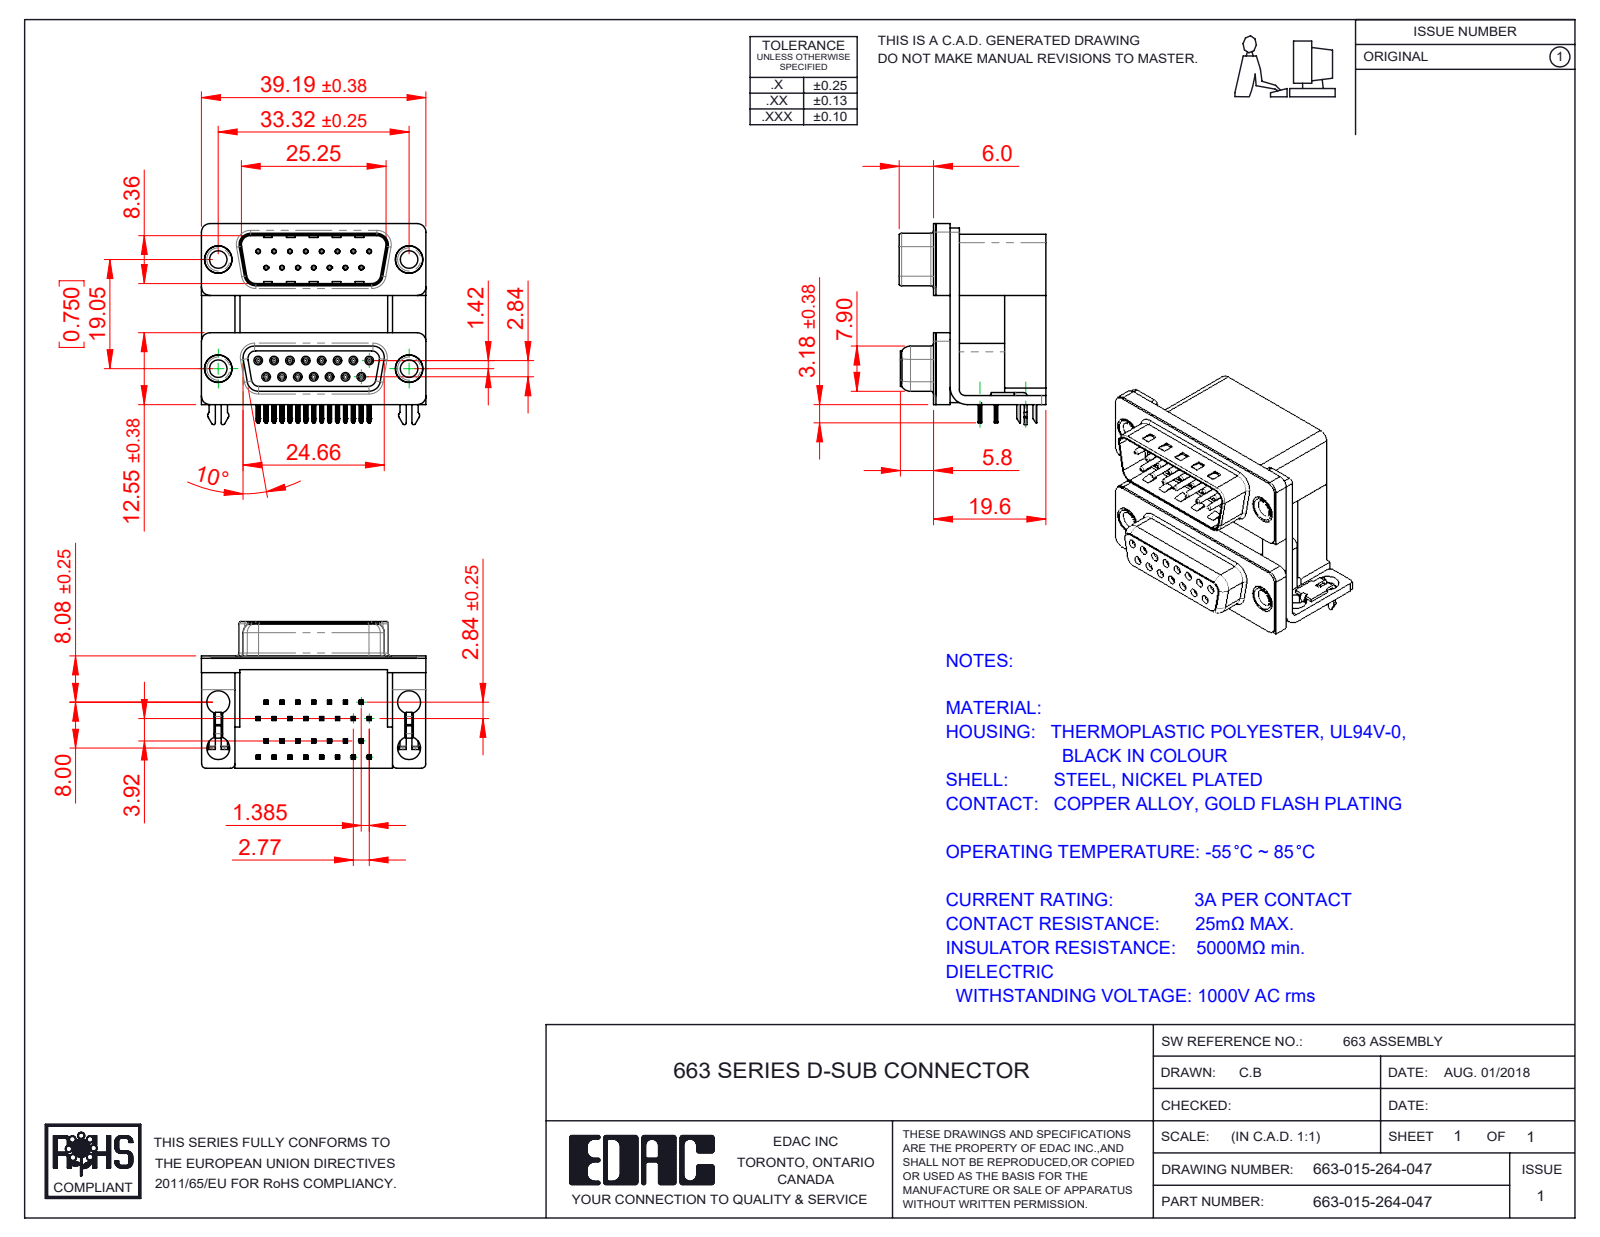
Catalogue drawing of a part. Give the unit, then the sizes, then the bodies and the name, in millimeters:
Units: millimetres
Overall size (bounding box): 39.19 × 35.1 × 25.6
Round holes (diameter × count): ⌀0.8 ×30, ⌀0.35 ×15, ⌀0.9 ×15, ⌀4 ×8, ⌀3.05 ×4, ⌀3.5 ×4, ⌀4.8 ×4, ⌀5 ×4
Round bosses / shafts (diameter × count): ⌀1.2 ×15, ⌀0.75 ×15, ⌀4.9 ×4, ⌀4.75 ×4, ⌀3.85 ×4
Partial cylindrical surfaces — rounded edges, fillets, slot ends (radius × count): R0.1 ×121, R0.25 ×66, R0.15 ×60, R0.12 ×30, R0.35 ×30, R0.5 ×16, R1.5 ×16, R0.34 ×15
Main face-to-face distances: 0.4, 19.2, 16.7, 2.5, 7.2, 12, 9.5, 10.69, 1.6, 2.9
Hole centre spacings: 3.16, 19.25, 2.77, 19.84, 5.54, 8.31, 19.05, 20.78
Volume: 15 197 mm³ · Surface area: 16 856 mm²
Bodies: 43 solids, 3936 faces (2093 planar, 1008 cylindrical, 835 other)
Part name (STEP PRODUCT): 663 Contact Bottom Upper_M; 663 Housing Lower_15 Contacts; 663 Mounting Bracket_2ProngM; 663 Contact Top Lower (+8 more)
STEP written by: SolidWorks 2020 (CONFIG_CONTROL_DESIGN)
